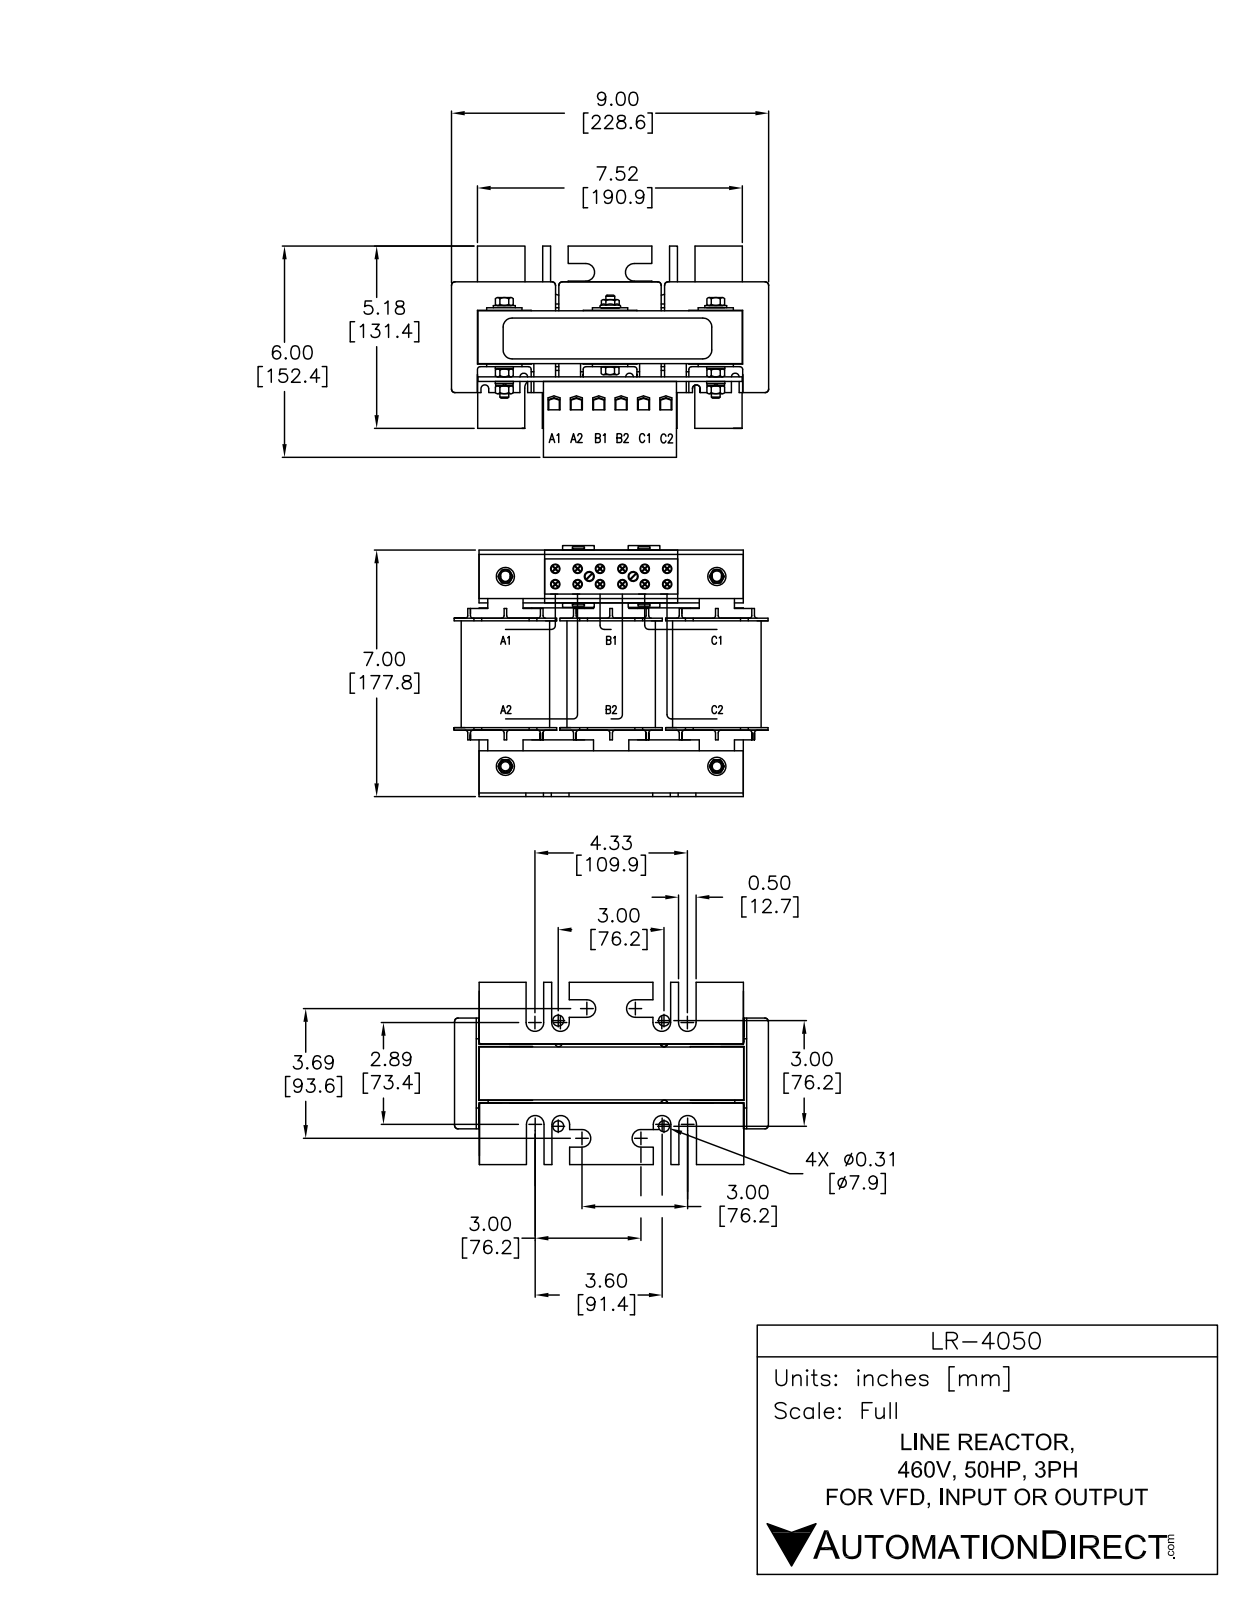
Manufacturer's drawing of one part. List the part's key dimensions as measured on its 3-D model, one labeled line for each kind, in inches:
Part name (STEP PRODUCT): LR-4050
STEP written by: SolidWorks 2011 (AUTOMOTIVE_DESIGN)
Units: inches
Bodies: 48 solids, 1510 faces (855 planar, 512 cylindrical, 143 other)
Overall size (bounding box): 8.937 × 6.996 × 5.371
Volume: 162.2 in³ · Surface area: 732.5 in²
Round holes (diameter × count): ⌀0.268 ×12, ⌀0.339 ×12, ⌀0.285 ×5
Round bosses / shafts (diameter × count): ⌀0.404 ×12, ⌀0.268 ×9, ⌀0.591 ×5, ⌀0.738 ×3, ⌀0.236 ×3, ⌀0.236 ×2
Partial cylindrical surfaces — rounded edges, fillets, slot ends (radius × count): R0.03 ×130, R0.039 ×12, R0.25 ×12, R0.276 ×12, R0.591 ×12, R0.134 ×11, R0.108 ×8, R0.185 ×5
Main face-to-face distances: 3.012, 0.079, 3.091, 0.276, 1.673, 1.496, 1.516, 0.384, 0.354, 3.366
Hole centre spacings: 0.63, 1.26, 1.608, 1.89, 0.884, 0.618, 0.62, 0.882
